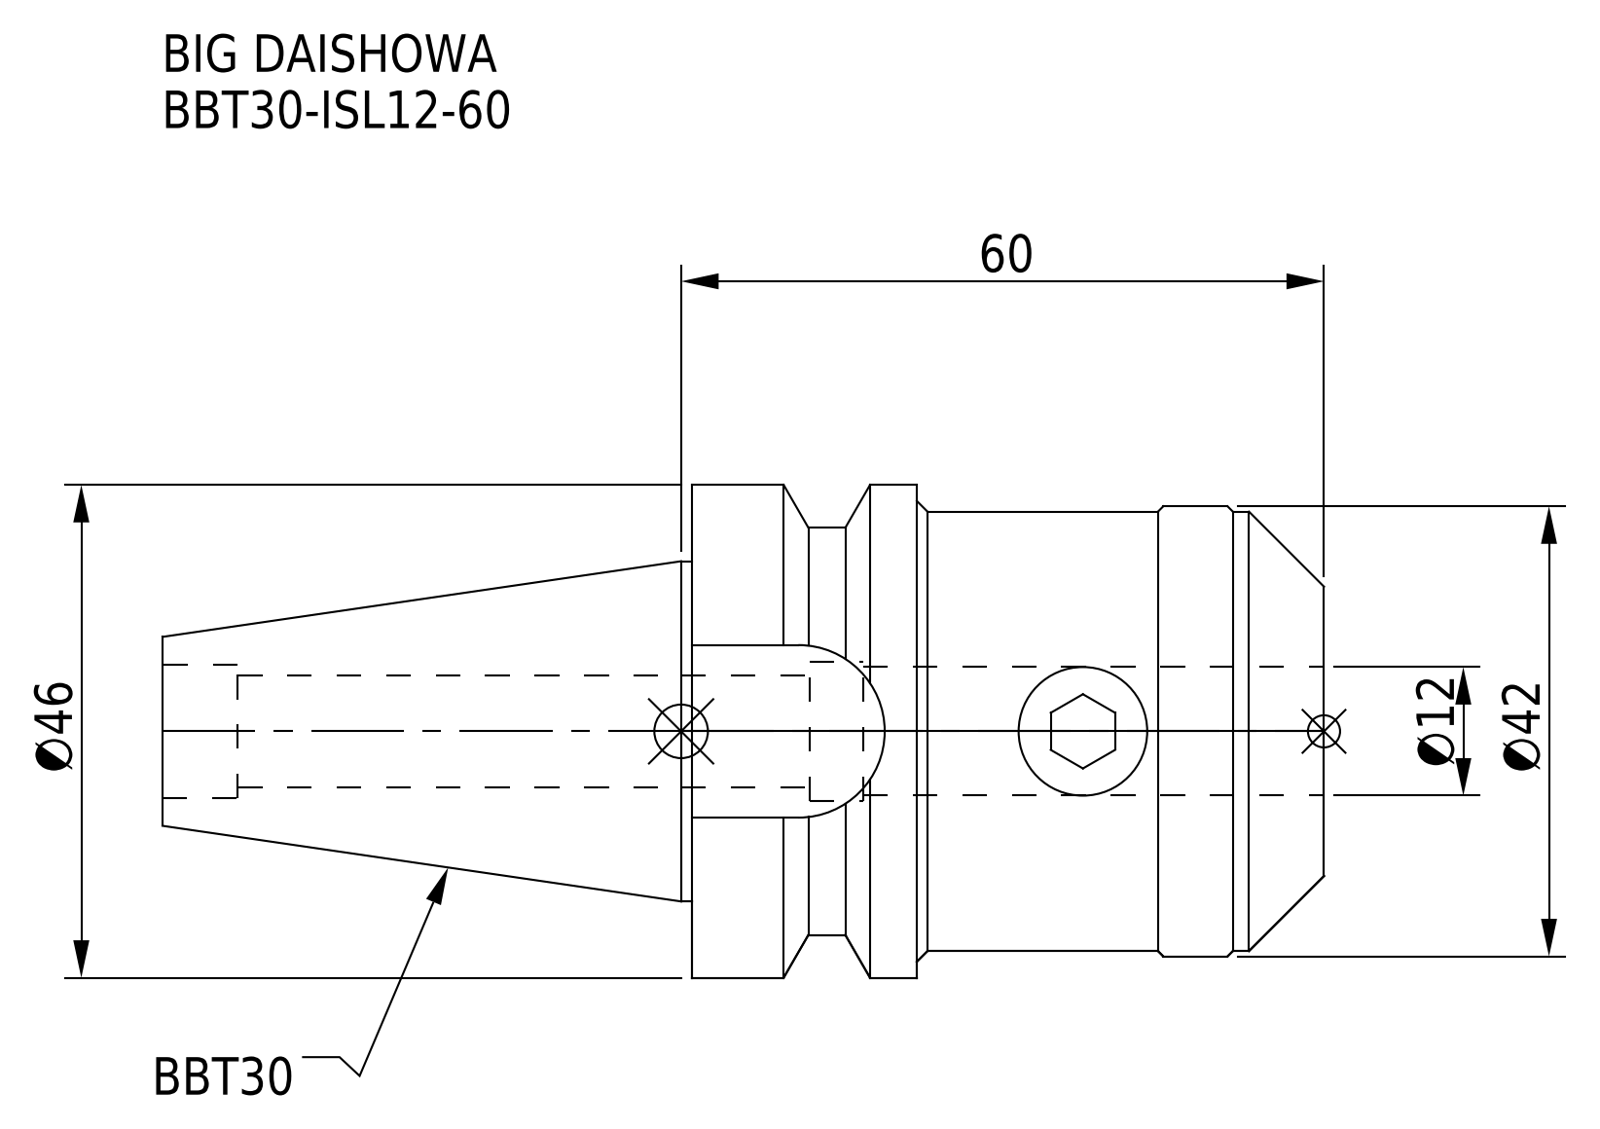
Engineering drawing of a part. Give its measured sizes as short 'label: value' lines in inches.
name: BBT30-ISL12-60
written by: CREO PARAMETRIC BY PTC INC, 2016380 (AUTOMOTIVE_DESIGN)
unit: in
bodies: 1 solid, 53 faces (13 planar, 26 cylindrical, 14 other)
size: 4.268 × 1.811 × 1.811
volume: 5.539 in³; area: 28.28 in²
holes: 1× ⌀0.409, 1× ⌀0.472, 1× ⌀0.492, 1× ⌀0.512
bosses: 1× ⌀1.811, 1× ⌀1.654, 1× ⌀1.614, 1× ⌀1.25
rounds: 1× R0.317, 1× R0.748
face distances: 2.323, 1.283, 1.496, 0.827, 4.268, 2.772, 1.945, 0.634, 1.89, 0.394
